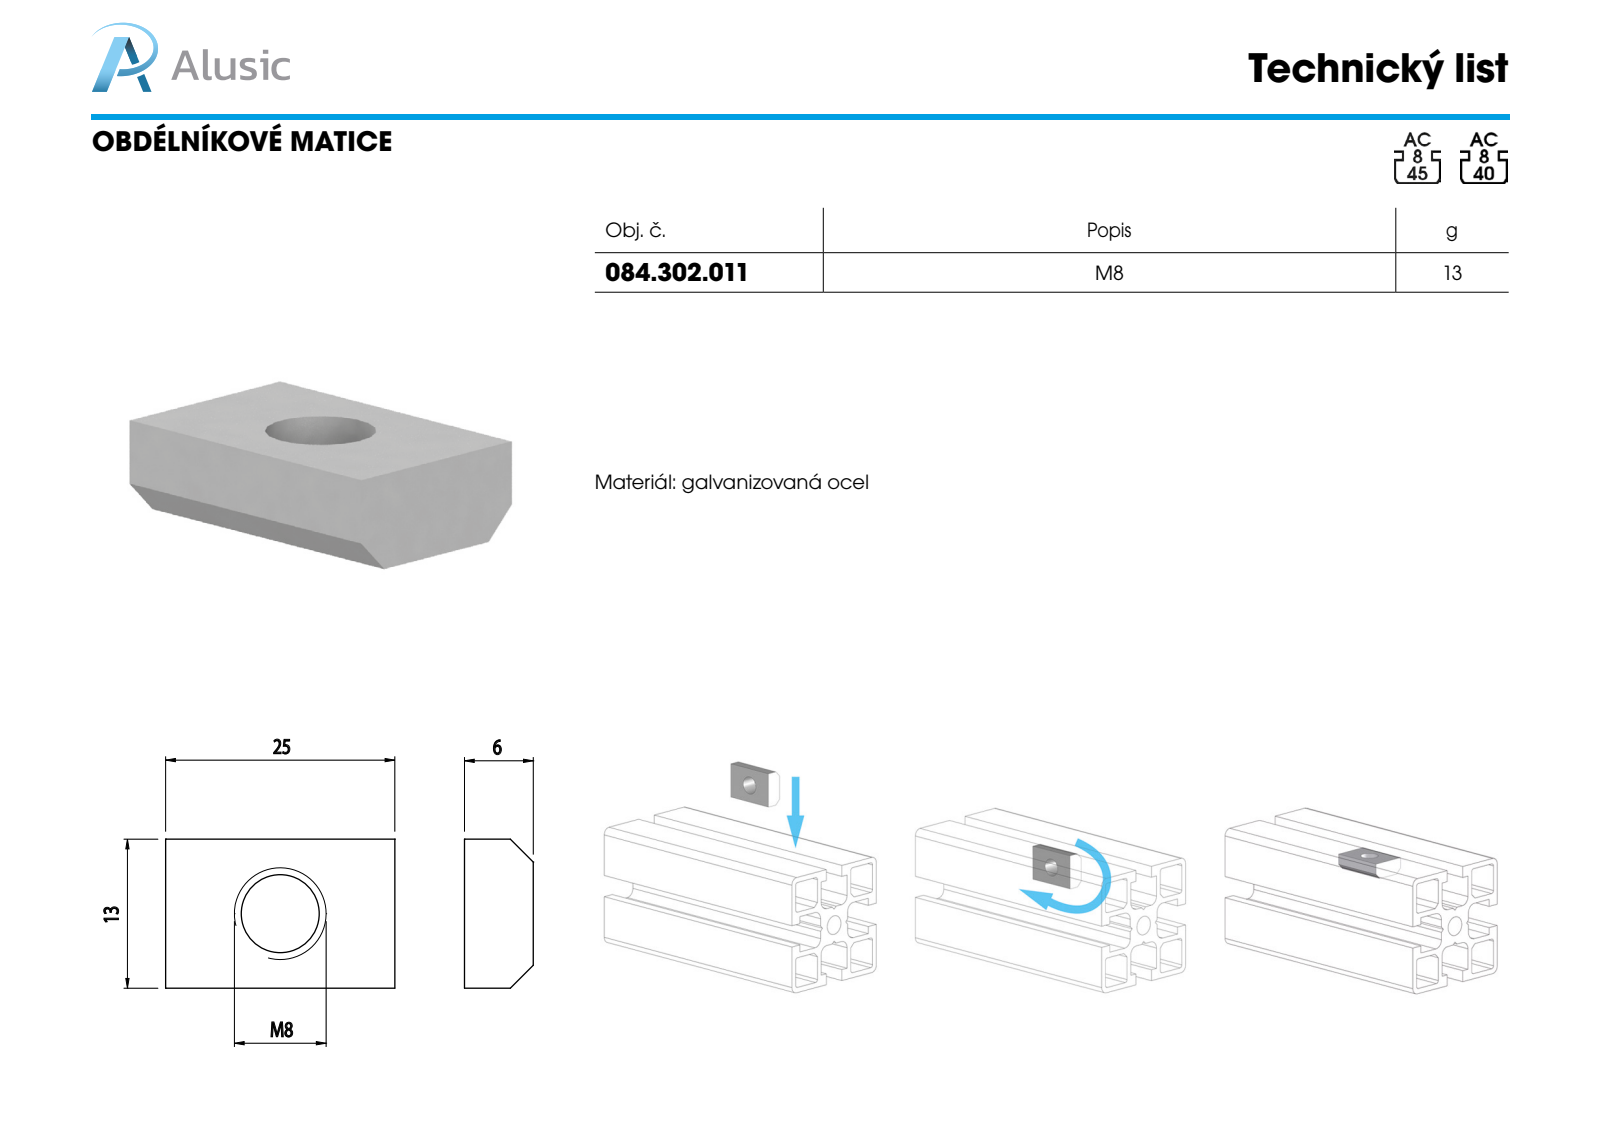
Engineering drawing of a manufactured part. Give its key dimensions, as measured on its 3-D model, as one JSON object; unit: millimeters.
{"part_name": "084.302.011", "step_written_by": "SolidWorks 2011 (CONFIG_CONTROL_DESIGN)", "units": "millimeters", "bodies": {"solids": 1, "faces": 10, "planar": 8, "cylindrical": 2, "other": 0}, "overall_size": [25, 13, 6], "volume_mm3": 1632, "surface_area_mm2": 1095, "round_holes": [[6.8, 1]], "face_to_face_distances": [6, 13, 25]}
